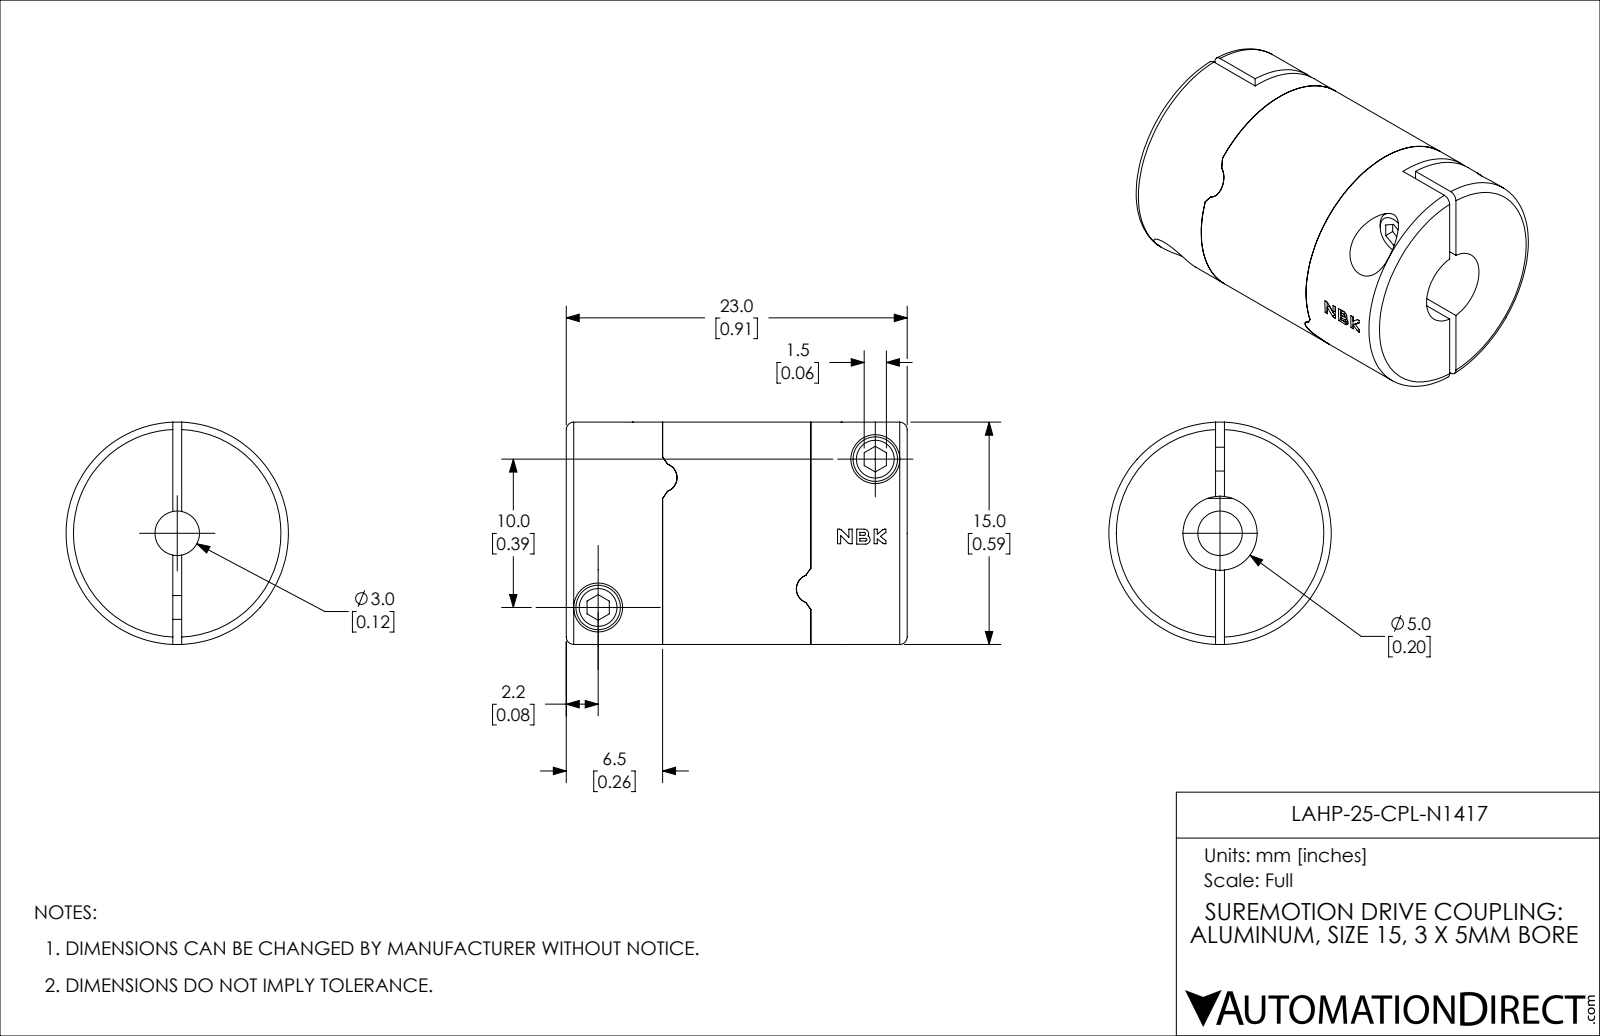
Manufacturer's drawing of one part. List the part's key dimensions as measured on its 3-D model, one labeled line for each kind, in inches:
Part name (STEP PRODUCT): LAHP-25-CPL-N1417
STEP written by: SolidWorks 2019 (CONFIG_CONTROL_DESIGN)
Units: inches
Bodies: 3 solids, 159 faces (89 planar, 56 cylindrical, 14 other)
Overall size (bounding box): 0.906 × 0.591 × 0.591
Volume: 0.21 in³ · Surface area: 4.65 in²
Round holes (diameter × count): ⌀0.063 ×2, ⌀0.079 ×2, ⌀0.13 ×2, ⌀0.118 ×1, ⌀0.197 ×1, ⌀0.217 ×1
Round bosses / shafts (diameter × count): ⌀0.118 ×2, ⌀0.591 ×1
Partial cylindrical surfaces — rounded edges, fillets, slot ends (radius × count): R0.008 ×4, R0.038 ×2, R0.012 ×1, R0.012 ×1
Main face-to-face distances: 0.256, 0.65, 0.394, 0.024, 0.175, 0.73, 0.081, 0.474, 0.152, 0.754
Hole centre spacings: 0.835
